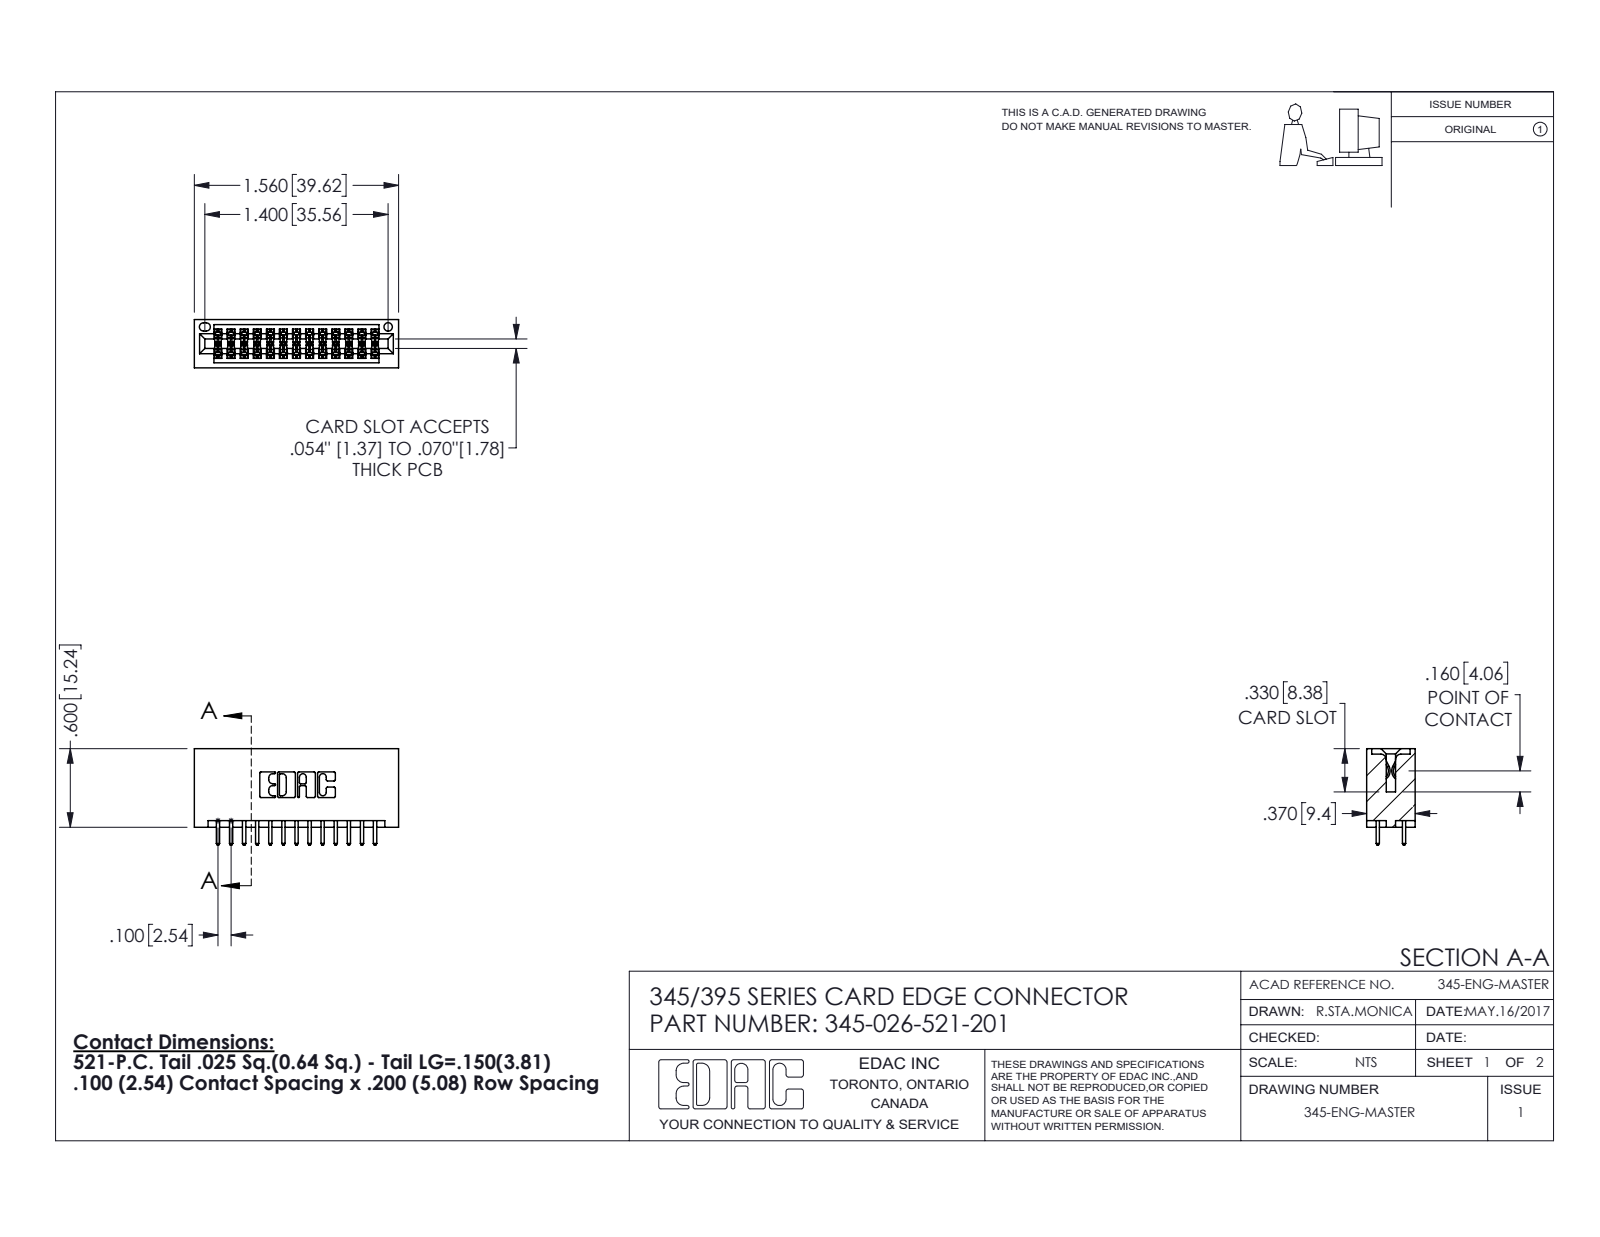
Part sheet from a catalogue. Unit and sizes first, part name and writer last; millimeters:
Units: millimetres
Overall size (bounding box): 39.6 × 18.7 × 9.4
Round holes (diameter × count): ⌀1.6 ×1
Partial cylindrical surfaces — rounded edges, fillets, slot ends (radius × count): R0.2 ×39, R0.3 ×26, R0.3 ×22, R0.2 ×6, R0.8 ×6, R0.7 ×3, R0.4 ×2, R0.5 ×2
Main face-to-face distances: 7.6, 1.8, 5.1, 9.4, 2.5, 6.9, 0.6, 5.7, 2.5, 7.6
Volume: 4 180 mm³ · Surface area: 5 859 mm²
Bodies: 27 solids, 1418 faces (934 planar, 484 cylindrical, 0 other)
Part name (STEP PRODUCT): 345 Part_No Mounting Lugs; 345-292-001_345-293-121; 345-026-521-201
STEP written by: SolidWorks 2016 (CONFIG_CONTROL_DESIGN)
